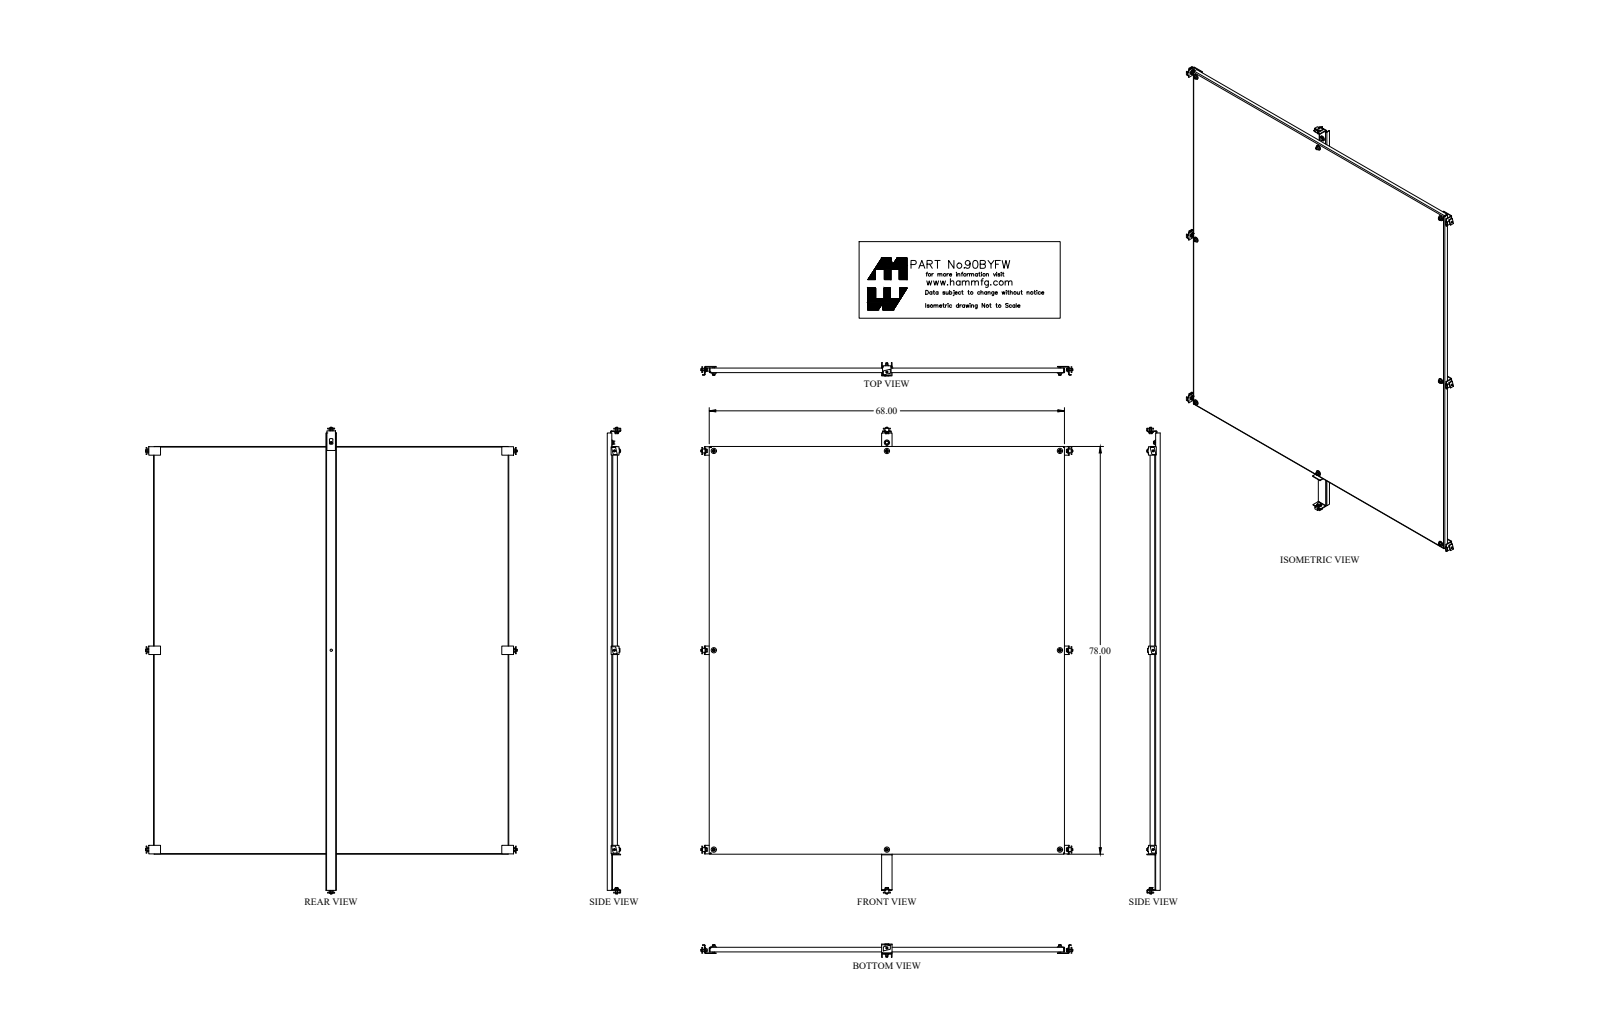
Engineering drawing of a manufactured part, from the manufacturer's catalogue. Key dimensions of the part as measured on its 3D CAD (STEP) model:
Part name (STEP PRODUCT): 90BYFW_Default
STEP written by: SolidWorks 2018 (CONFIG_CONTROL_DESIGN)
Units: inches
Bodies: 1 solid, 70 faces (38 planar, 24 cylindrical, 8 other)
Overall size (bounding box): 78 × 68 × 0.875
Volume: 688.1 in³ · Surface area: 11 049 in²
Round holes (diameter × count): ⌀0.563 ×8
Partial cylindrical surfaces — rounded edges, fillets, slot ends (radius × count): R0.06 ×4, R0.185 ×4
Main face-to-face distances: 0.125, 0.125, 67.875, 77.875, 67.75, 68, 77.75, 78, 0.875, 0.75
Hole centre spacings: 33.125, 38.125, 50.506, 76.437, 83.135, 66.25, 76.25, 101.011
